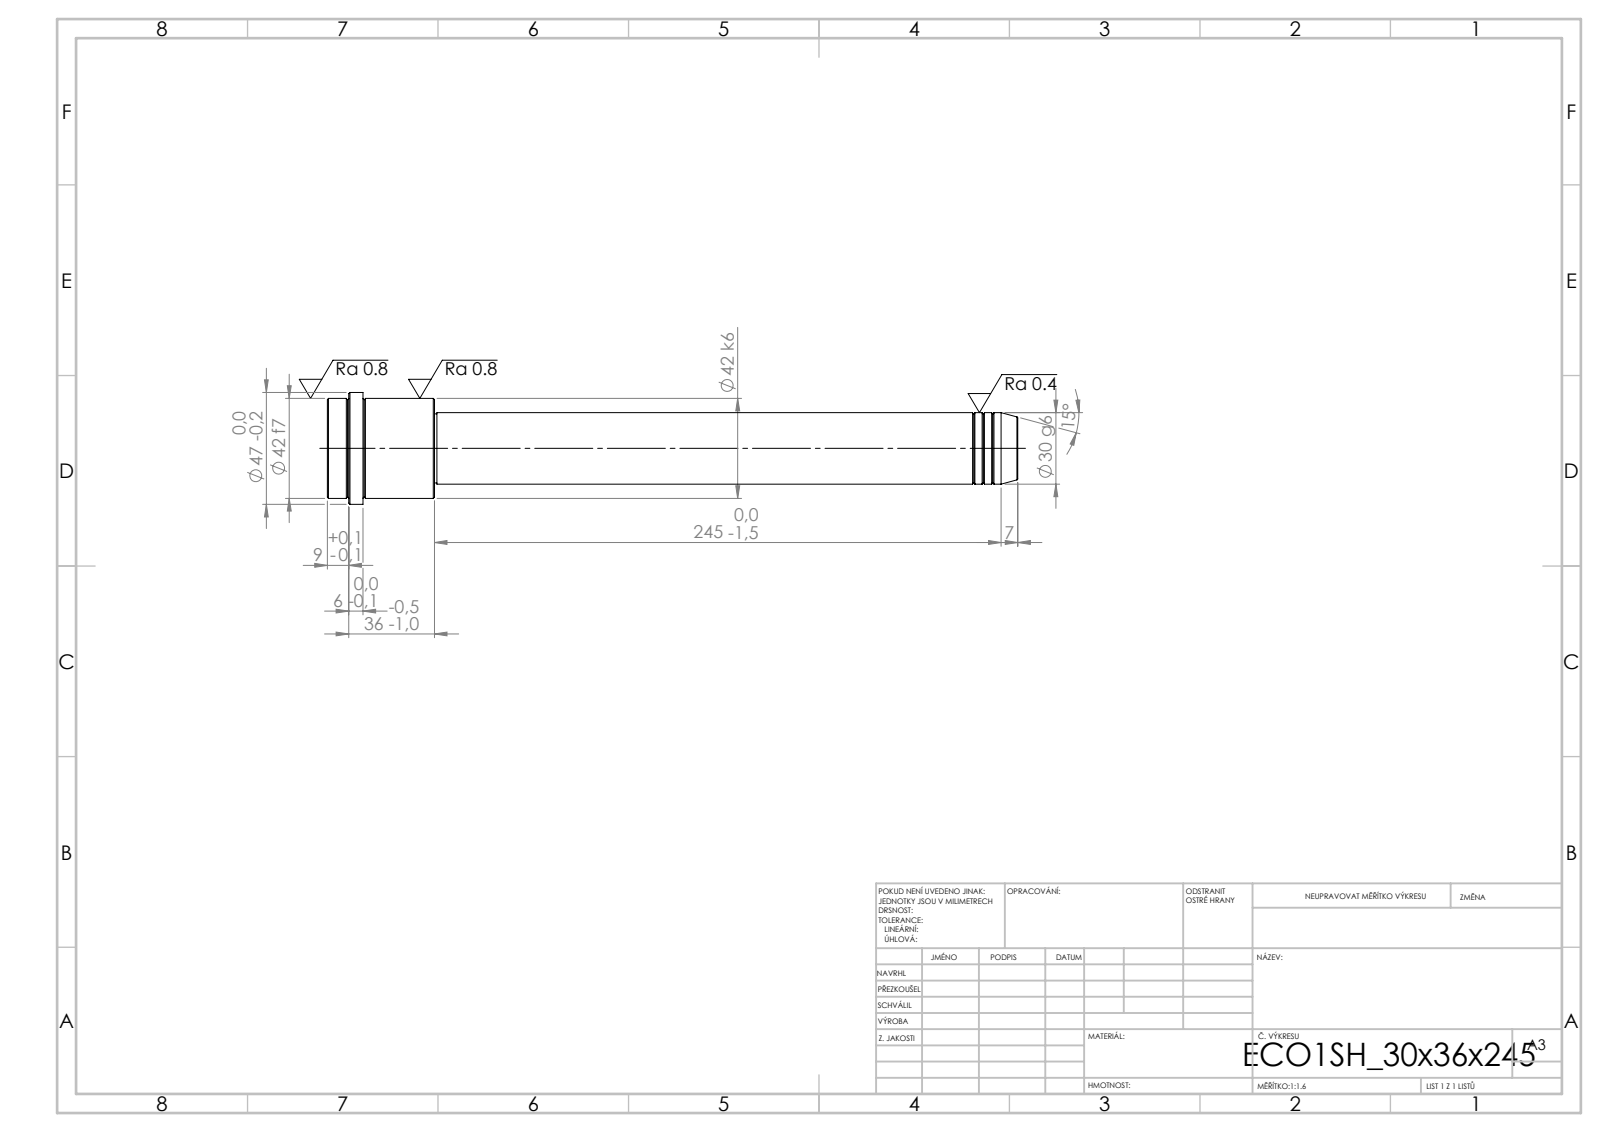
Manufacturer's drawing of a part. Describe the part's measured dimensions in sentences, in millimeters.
Its 3-D file was written by "SolidWorks 2019 (CONFIG_CONTROL_DESIGN)". It is 1 solid with 52 faces: 6 planar, 16 cylindrical and 30 other. Overall it measures 290 by 47 by 47 millimeters. Its volume is 236 718 cubic millimeters and its surface area 32 662 square millimeters. Round bosses or shafts: 1 of diameter 47, 1 of diameter 42, 1 of diameter 30, 1 of diameter 29. The main face-to-face distances are 45, 245, 290, 275, 30, 15, 281, 36, 6, 9.
